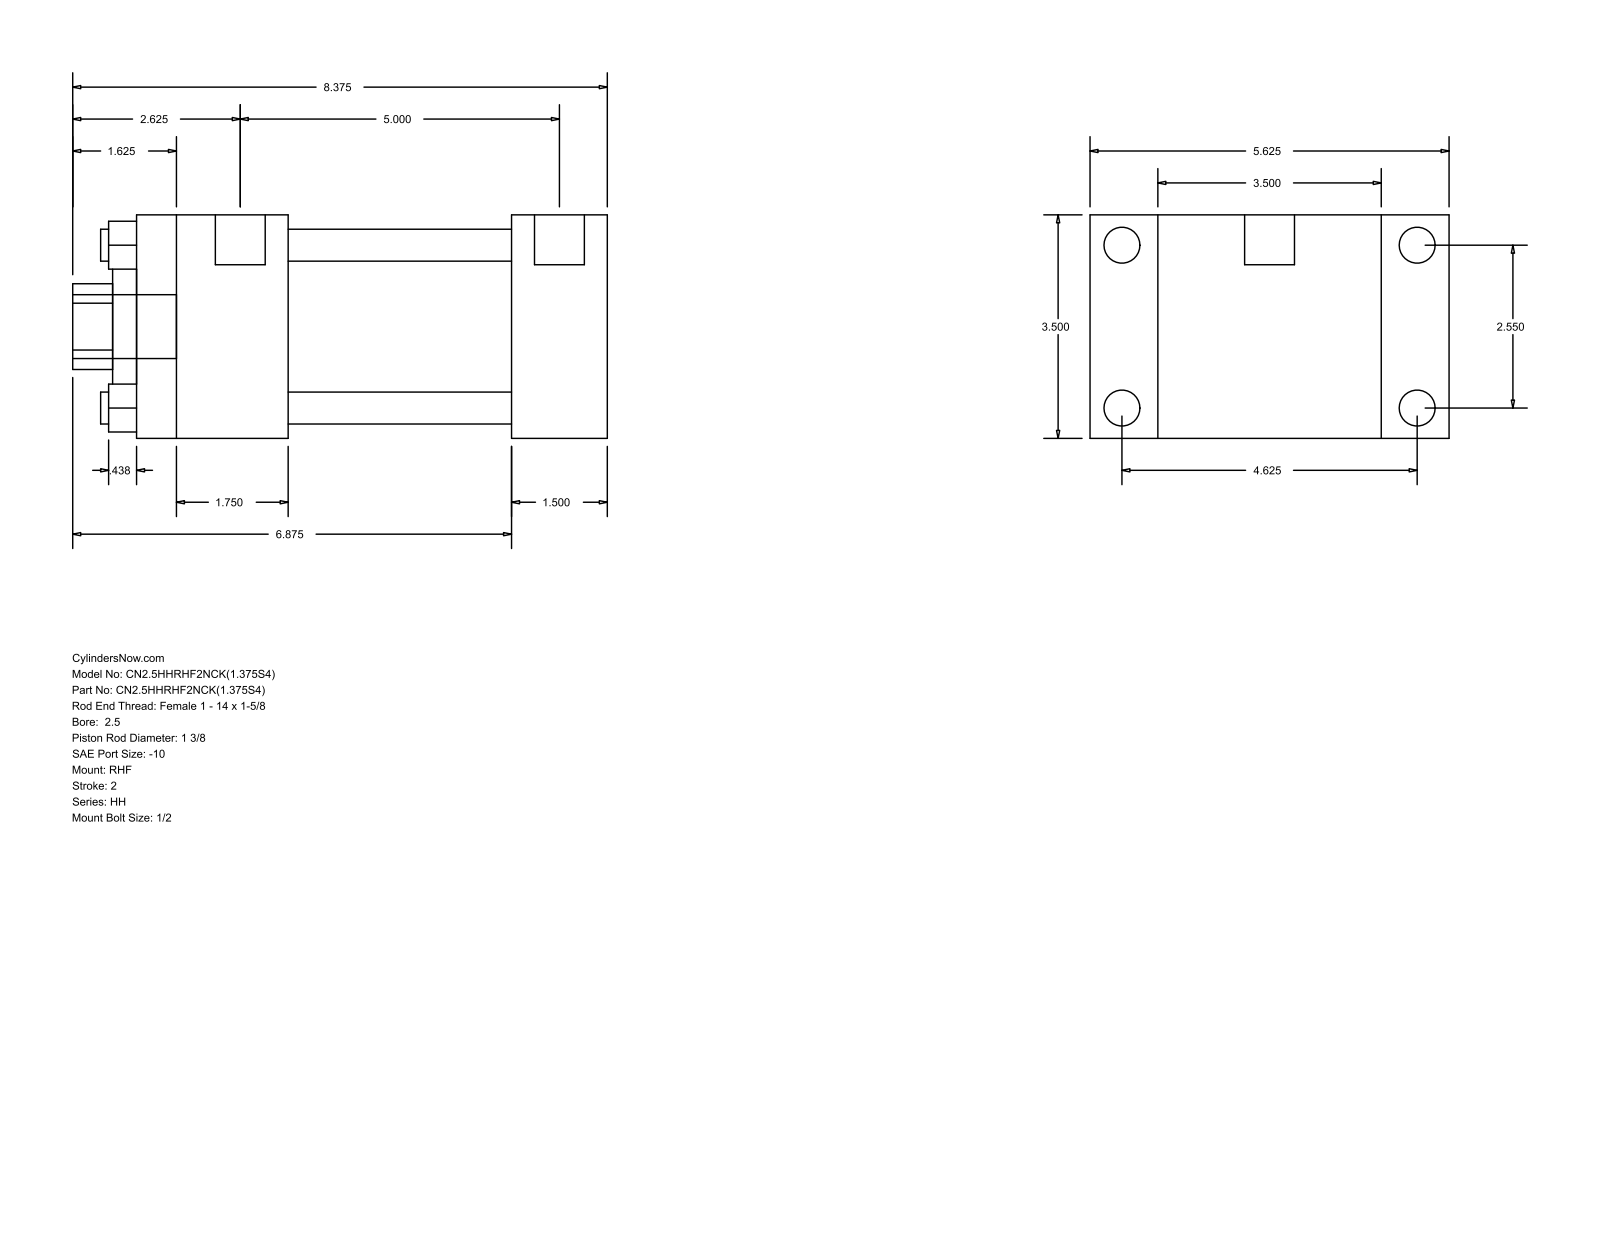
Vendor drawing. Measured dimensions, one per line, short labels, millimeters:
name: HH_RHF__0250_1.375
written by: GSSL Pune (CONFIG_CONTROL_DESIGN)
unit: mm
bodies: 0 solids, 88 faces (60 planar, 28 cylindrical, 0 other)
size: 212.72 × 142.88 × 88.9
holes: 4× ⌀12.7, 1× ⌀34.92, 1× ⌀50.8, 1× ⌀73.03
bosses: 4× ⌀14.3, 4× ⌀5.56, 2× ⌀19.84, 1× ⌀25.4
rounds: 1× R17.06
face distances: 88.9, 38.1, 26.99, 115.89, 149.22, 187.32, 142.88, 60.32, 127, 19.05
hole spacings: 45.79, 64.76, 91.58
